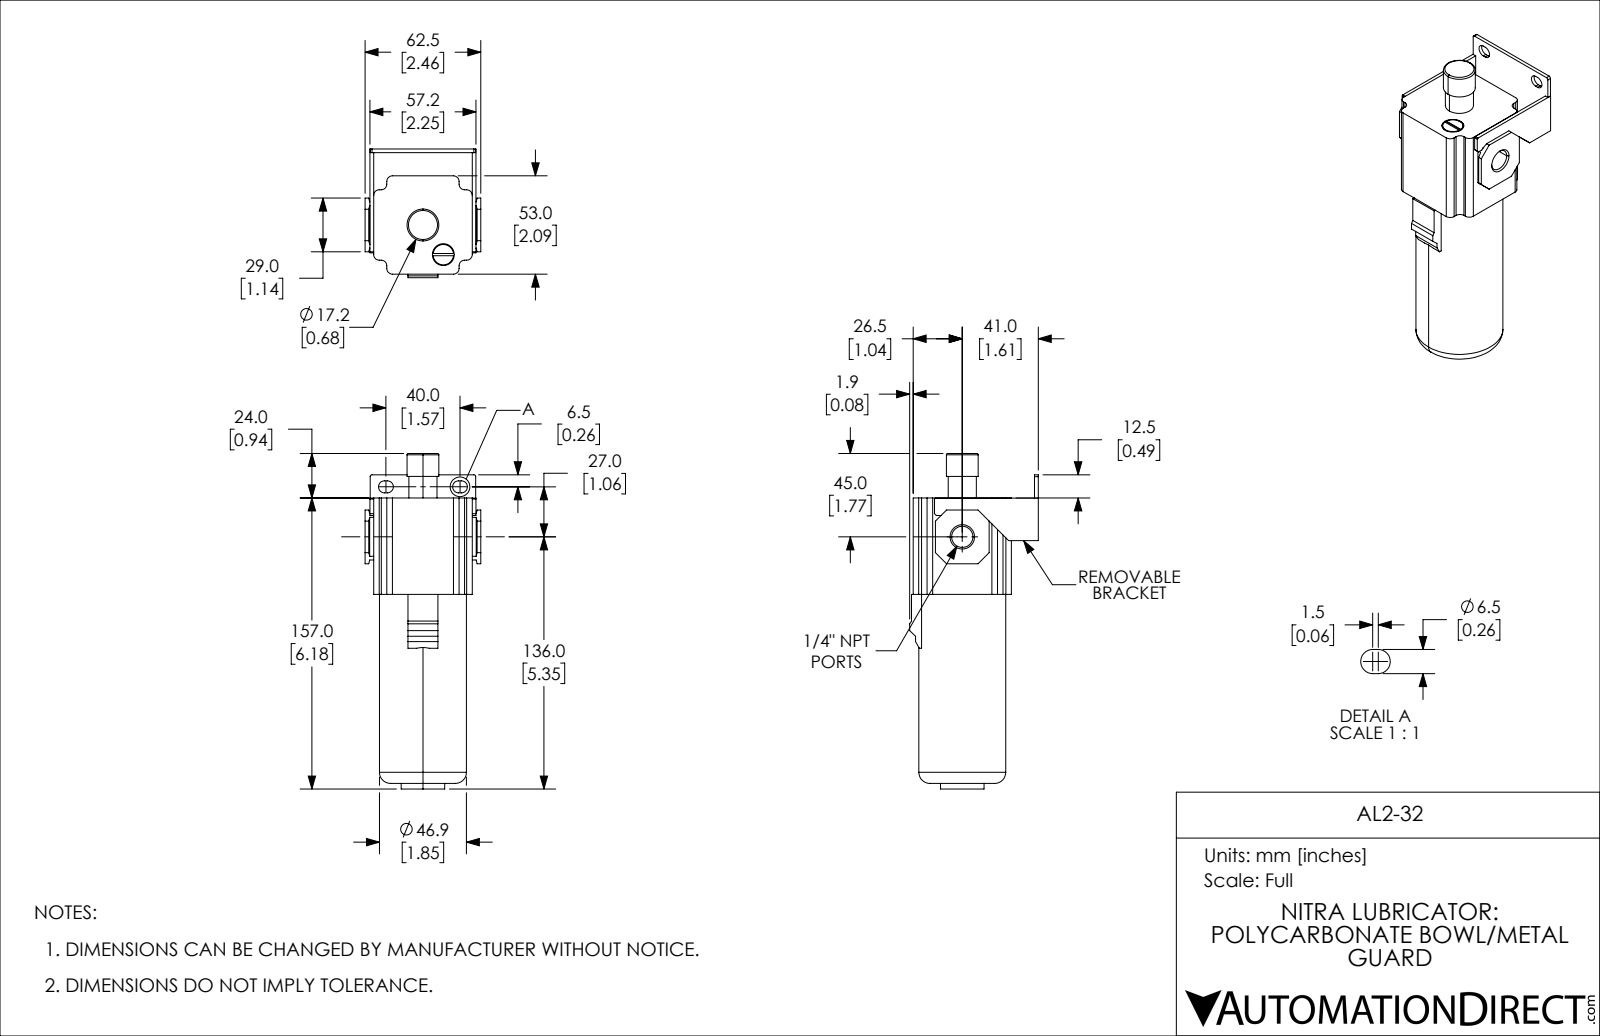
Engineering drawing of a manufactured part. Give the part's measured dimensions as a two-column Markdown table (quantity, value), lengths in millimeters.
| quantity | value |
| --- | --- |
| part name | AL2-32 |
| STEP written by | SolidWorks 2019 (CONFIG_CONTROL_DESIGN) |
| units | millimeters |
| bodies | 1 solid, 138 faces (96 planar, 34 cylindrical, 8 other) |
| overall size | 181 × 69.42 × 62.5 |
| volume | 329 034 mm³ |
| surface area | 40 761 mm² |
| round holes (diameter × count) | 11.45 × 1, 11.8 × 1 |
| round bosses / shafts (diameter × count) | 46.9 × 1, 23.5 × 1, 17.2 × 1, 15.2 × 1, 11 × 1 |
| partial cylindrical surfaces (radius × count) | 3 × 12, 3.25 × 4, 1 × 2 |
| main face-to-face distances | 2, 12.5, 14.5, 67.5, 65.5, 53, 55.2, 2.65, 4.65, 57.85 |
